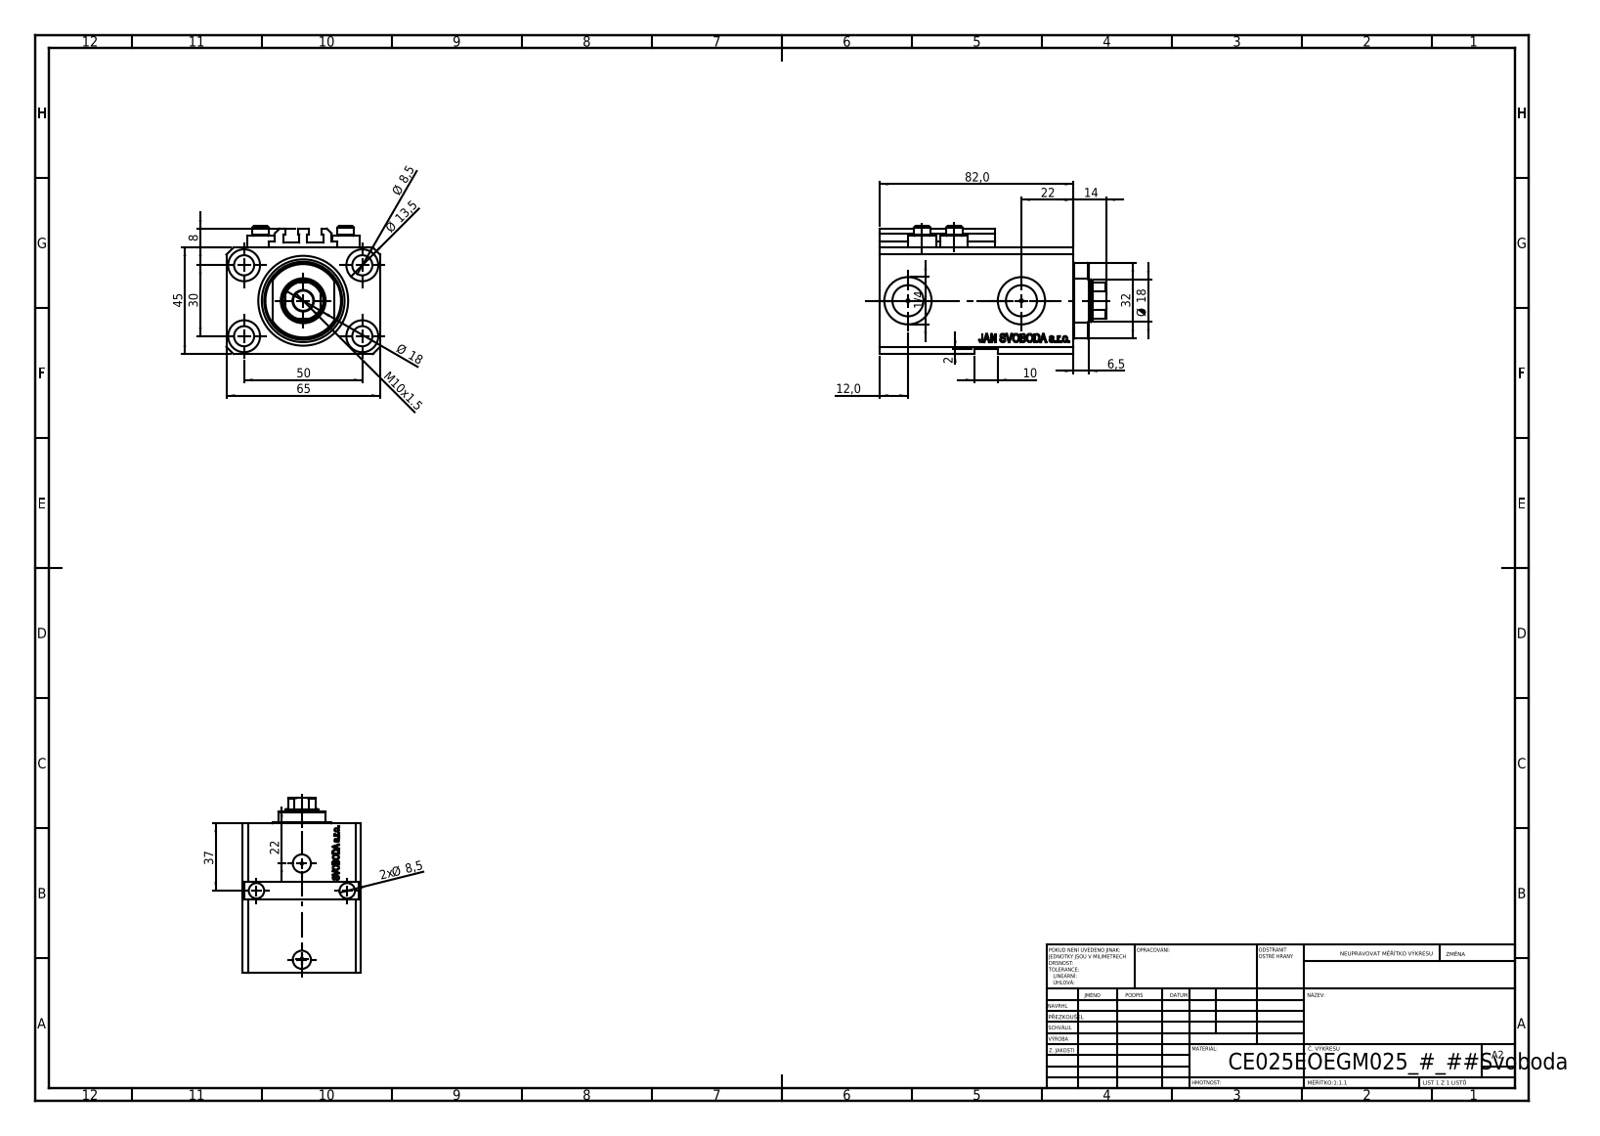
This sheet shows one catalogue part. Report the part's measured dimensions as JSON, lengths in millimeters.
{"part_name": "V250CE_C_VCP; V250CE_VC_E; ALLEN BOLT V250CE; V250CE_E_Body", "step_written_by": "SolidWorks 2019 (CONFIG_CONTROL_DESIGN)", "units": "millimeters", "bodies": {"solids": 8, "faces": 1067, "planar": 511, "cylindrical": 126, "other": 430}, "overall_size": [96, 65, 54], "volume_mm3": 212624, "surface_area_mm2": 61964, "round_holes": [[8.5, 7], [1.25, 4], [4, 4], [13.5, 4], [10, 2], [13.16, 2], [20, 2], [18, 1], [25, 1], [38, 1]], "round_bosses_or_shafts": [[11.6, 4], [7, 4]], "partial_cylinders_radius": [[0.2, 10], [8.5, 1], [16, 1]], "face_to_face_distances": [45, 65, 68, 14, 82, 2, 3, 47, 6.9, 61.1], "hole_center_spacings": [29.15, 45.04, 50, 13.6, 15.12, 20.82, 21.1, 27.89]}
